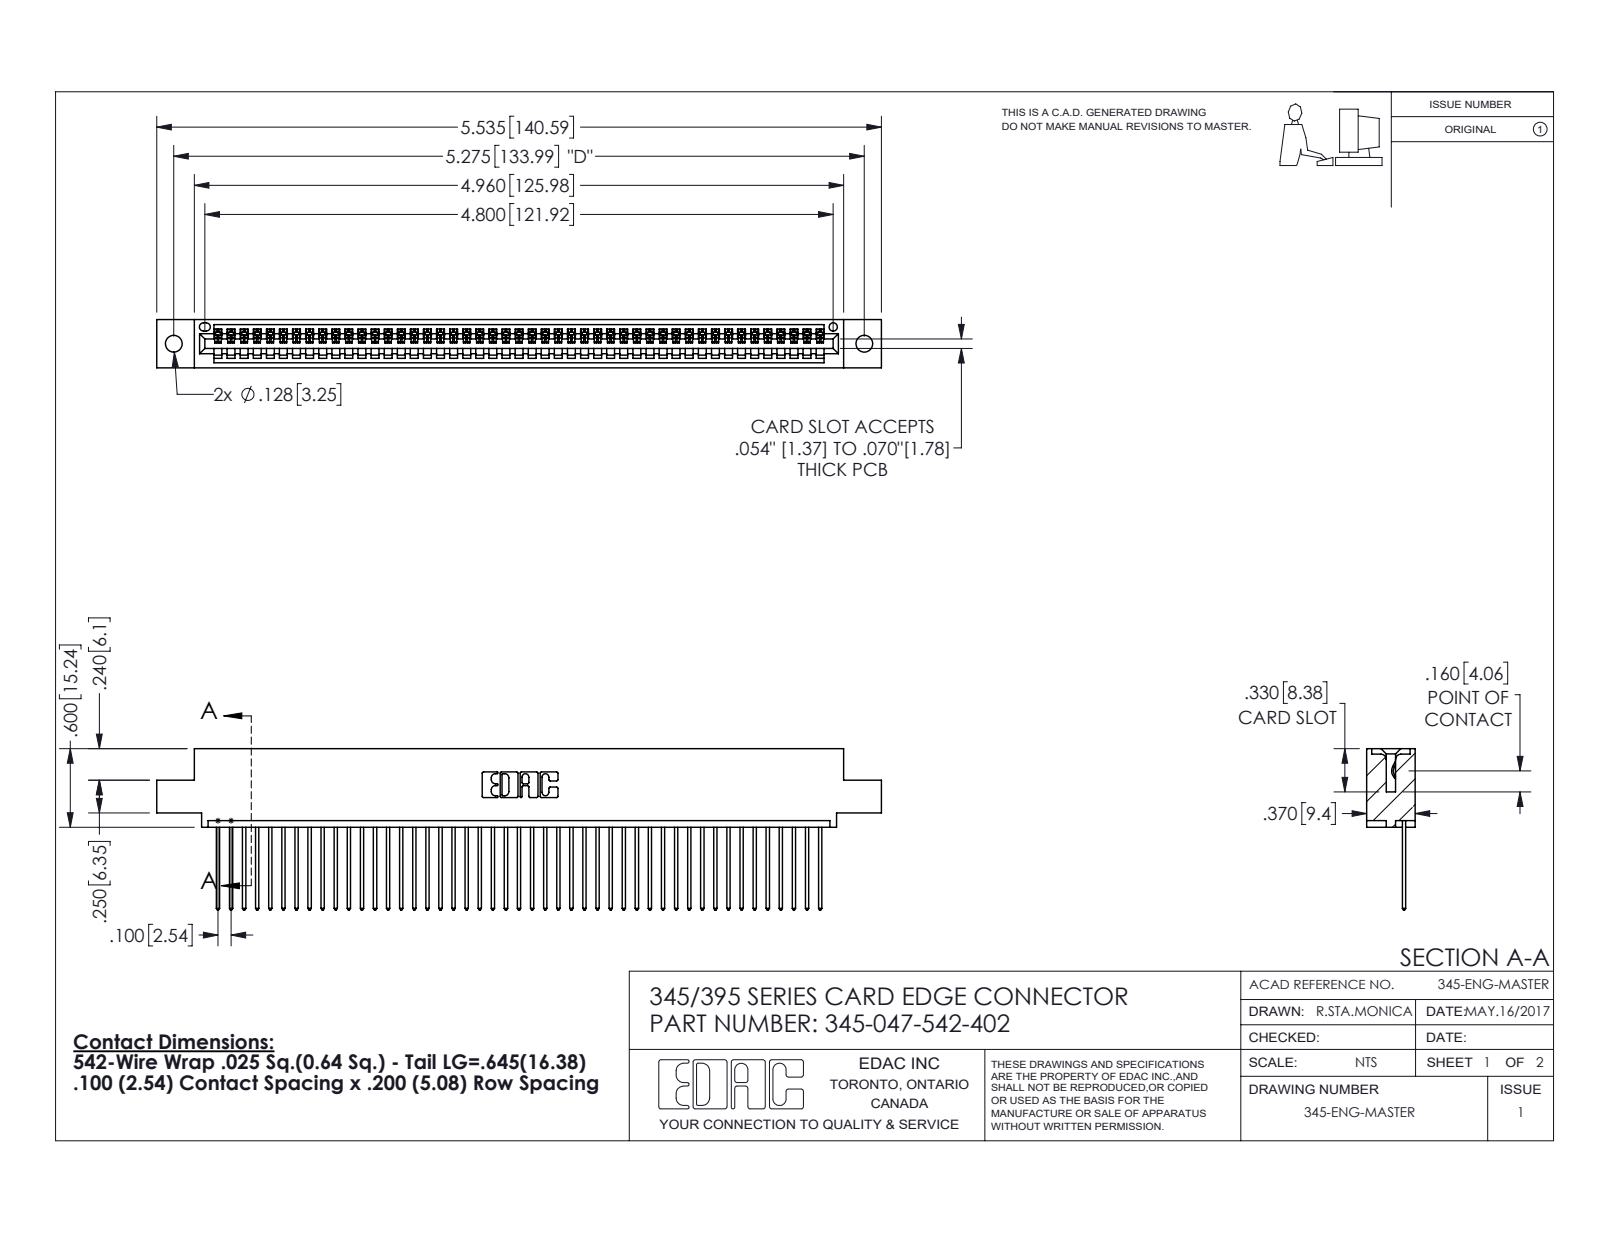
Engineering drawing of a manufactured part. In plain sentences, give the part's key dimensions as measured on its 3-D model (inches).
The part is named "345 Part_0.110 Offset - 0.128 Dia; 345-292-001_345-293-142; 345-047-542-402". Its 3-D file was written by "SolidWorks 2016 (CONFIG_CONTROL_DESIGN)". It is 48 solids with 2856 faces: 1964 planar, 892 cylindrical and 0 other. Overall it measures 5.535 by 1.232 by 0.37 inches. Its volume is 0.817 cubic inches and its surface area 28.41 square inches. Round holes: 2 of diameter 0.128, 1 of diameter 0.064. Partial cylindrical surfaces (rounded edges, fillets, slot ends): 94 of radius 0.006, 94 of radius 0.01, 22 of radius 0.01, 6 of radius 0.007, 6 of radius 0.031, 3 of radius 0.026, 2 of radius 0.031, 2 of radius 0.04. The main face-to-face distances are 0.072, 0.298, 0.098, 0.272, 0.025, 0.37, 0.2, 0.225, 0.149, 0.072. The hole center spacings are 0.27, 5.039, 5.275.
